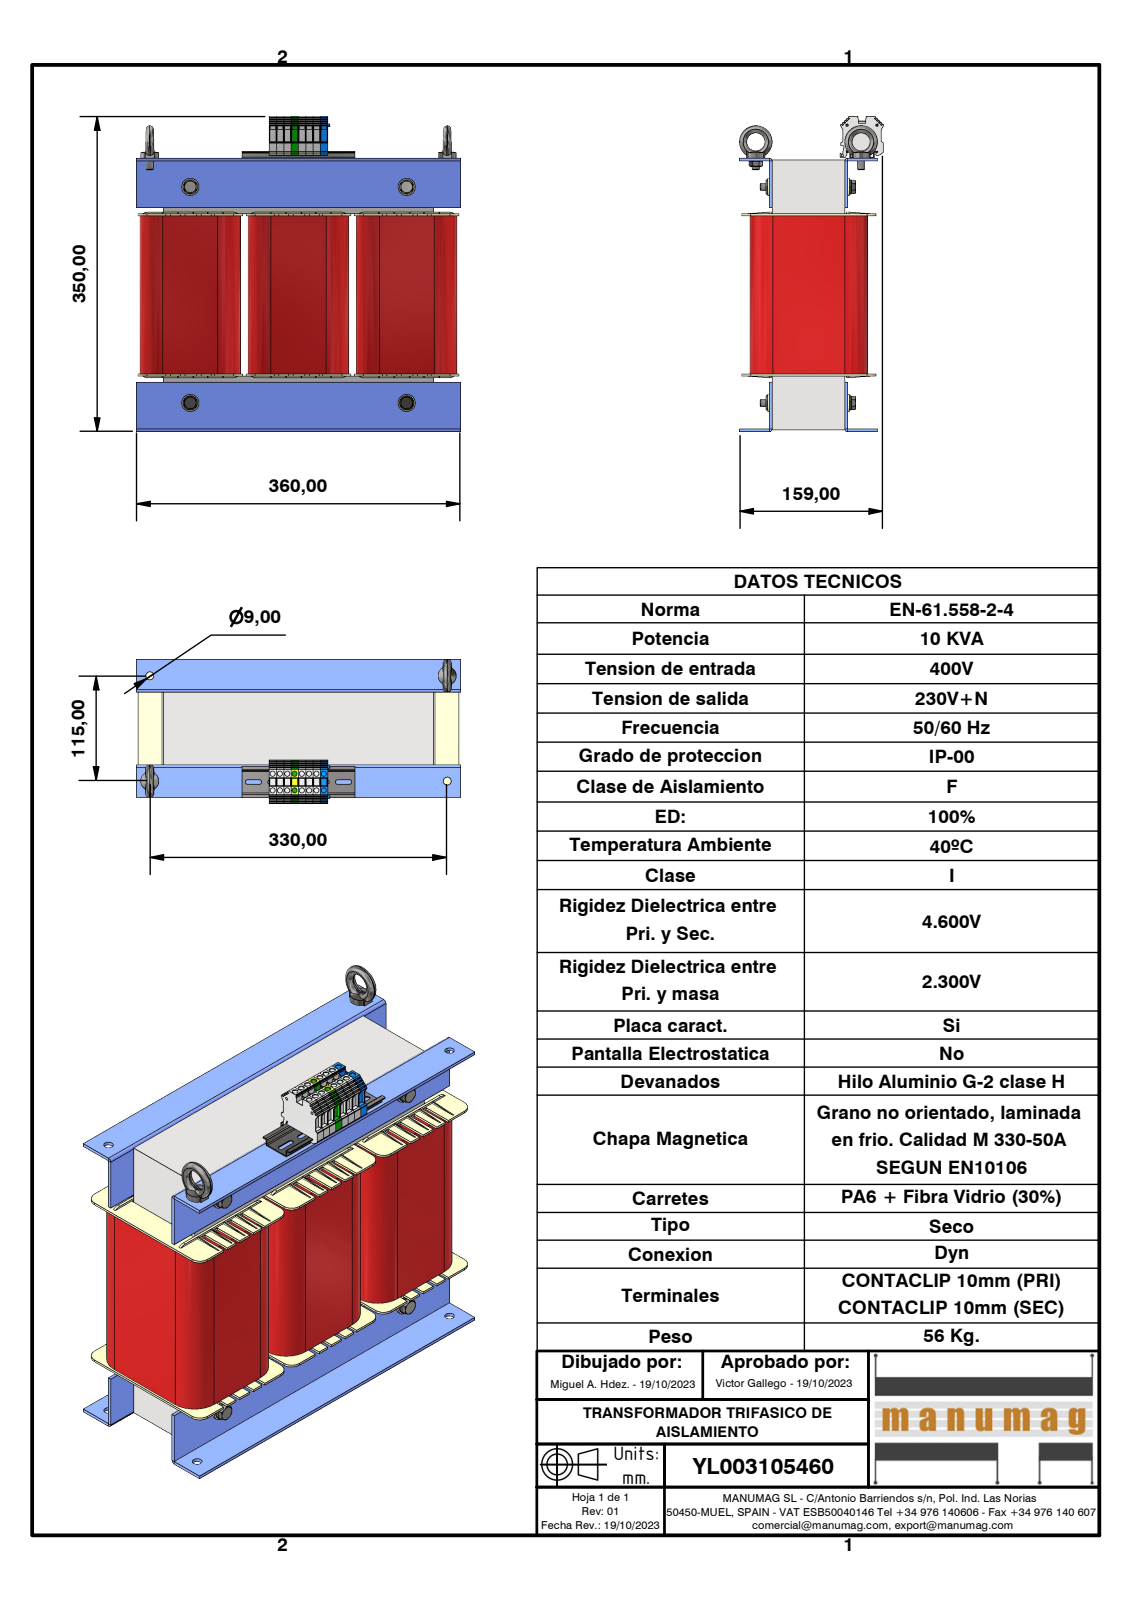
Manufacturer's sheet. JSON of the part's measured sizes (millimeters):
{"part_name": "YL003105460; UI 180 - 80 (300x300); UI 180_80_BOBINADO; RC60 NT060 (+8 more)", "step_written_by": "Autodesk Inventor 2023 (AUTOMOTIVE_DESIGN)", "units": "millimeters", "bodies": {"solids": 40, "faces": 3319, "planar": 2358, "cylindrical": 793, "other": 168}, "overall_size": [360, 350.5, 158.93], "volume_mm3": 10570000, "surface_area_mm2": 1490000, "round_holes": [[5.7, 16], [8, 4], [8.4, 4], [9, 4], [10.5, 4], [11, 4], [2.4, 2], [2.5, 2], [2.75, 2], [20, 2], [6.65, 1]], "round_bosses_or_shafts": [[19, 4], [16, 4], [11.4, 4], [9.6, 4], [7.32, 4], [36, 2], [8, 2], [7, 2]], "partial_cylinders_radius": [[0.3, 81], [1, 28], [10, 26], [2, 17], [3, 12], [3.31, 12], [25.37, 12], [2.6, 10]], "face_to_face_distances": [1, 2, 3, 83, 120, 60, 22.37, 23.37, 80, 240], "hole_center_spacings": [8.1, 20.1, 16.2, 24.52, 24.3, 30.48, 18.4, 32.4]}
